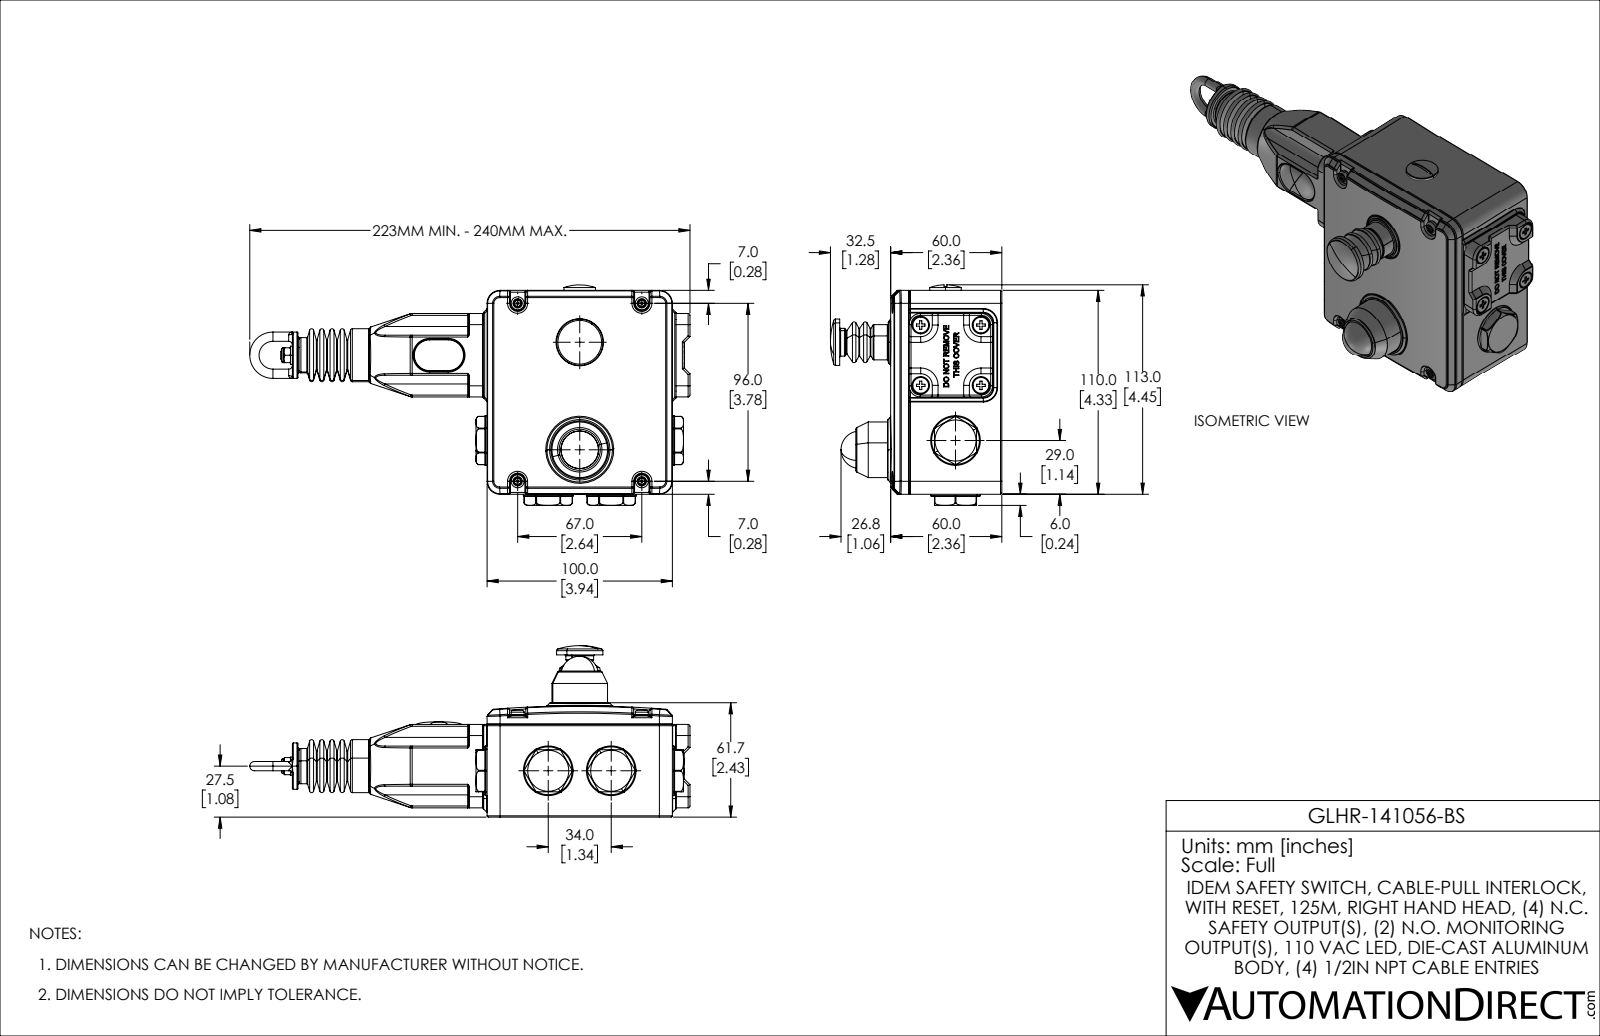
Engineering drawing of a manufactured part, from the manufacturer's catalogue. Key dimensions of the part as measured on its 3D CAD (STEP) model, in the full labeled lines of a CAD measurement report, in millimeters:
Part name (STEP PRODUCT): GLHR-141056-BS
STEP written by: SolidWorks 2021 (AUTOMOTIVE_DESIGN)
Units: millimetres
Bodies: 41 solids, 4536 faces (1445 planar, 1449 cylindrical, 1642 other)
Overall size (bounding box): 237.6 × 119 × 92.5
Volume: 300 000 mm³ · Surface area: 184 200 mm²
Round holes (diameter × count): ⌀5 ×10, ⌀5.3 ×9, ⌀9.5 ×7, ⌀9 ×5, ⌀3.3 ×4, ⌀4 ×4, ⌀4.8 ×4, ⌀5.4 ×4, ⌀5.8 ×4, ⌀1.7 ×3, ⌀2.6 ×3, ⌀3 ×3
Round bosses / shafts (diameter × count): ⌀8.5 ×7, ⌀6 ×7, ⌀4.4 ×7, ⌀5 ×6, ⌀7 ×5, ⌀3.5 ×4, ⌀1.3 ×4, ⌀26.8 ×3
Partial cylindrical surfaces — rounded edges, fillets, slot ends (radius × count): R0.5 ×241, R1 ×158, R0.2 ×76, R0.7 ×72, R0.3 ×26, R0.2 ×14, R6 ×12, R0.1 ×10
Main face-to-face distances: 3.5, 54.8, 2.9, 51.9, 110, 1.4, 2, 4, 102, 98.5
Hole centre spacings: 32.5, 32.5, 5.8, 9.5, 23, 48, 48.6, 76.5
